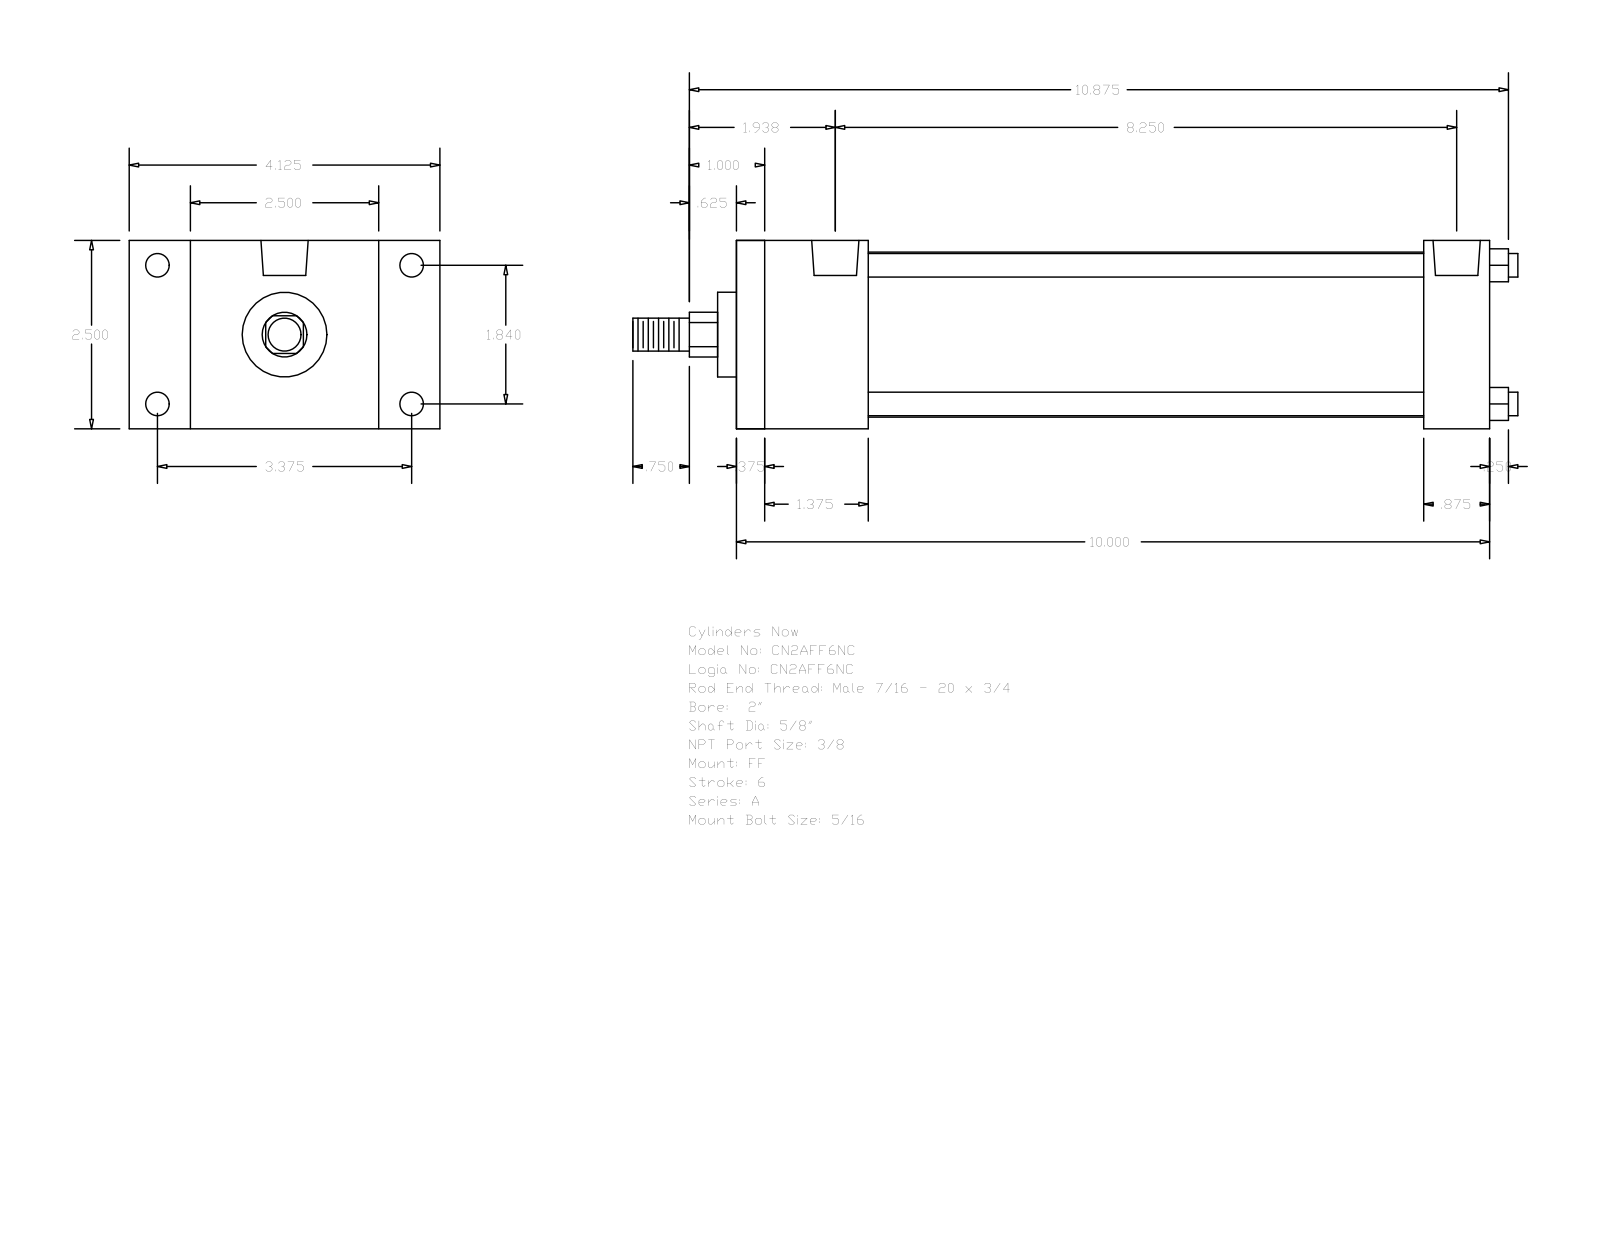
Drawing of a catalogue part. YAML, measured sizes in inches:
part_name: "A_FF__0200_0.625"
step_written_by: "GSSL Pune (CONFIG_CONTROL_DESIGN)"
units: inches
bodies: {solids: 0, faces: 92, planar: 64, cylindrical: 28, other: 0}
overall_size: [11.75, 4.125, 2.5]
round_holes:
  - {diameter: 0.219, count: 4}
  - {diameter: 0.313, count: 4}
  - {diameter: 0.627, count: 2}
round_bosses_or_shafts:
  - {diameter: 0.313, count: 4}
  - {diameter: 2.19, count: 1}
  - {diameter: 1.125, count: 1}
  - {diameter: 0.625, count: 1}
  - {diameter: 0.437, count: 1}
partial_cylinders:
  - {radius: 0.297, count: 1}
face_to_face_distances: [2.5, 10, 0.375, 9.625, 1.375, 1.75, 9.125, 8.75, 7.375, 8.25]
hole_center_spacings: [1.84, 3.375, 3.844, 7.937, 0.156, 0.157, 8.093, 8.094]
